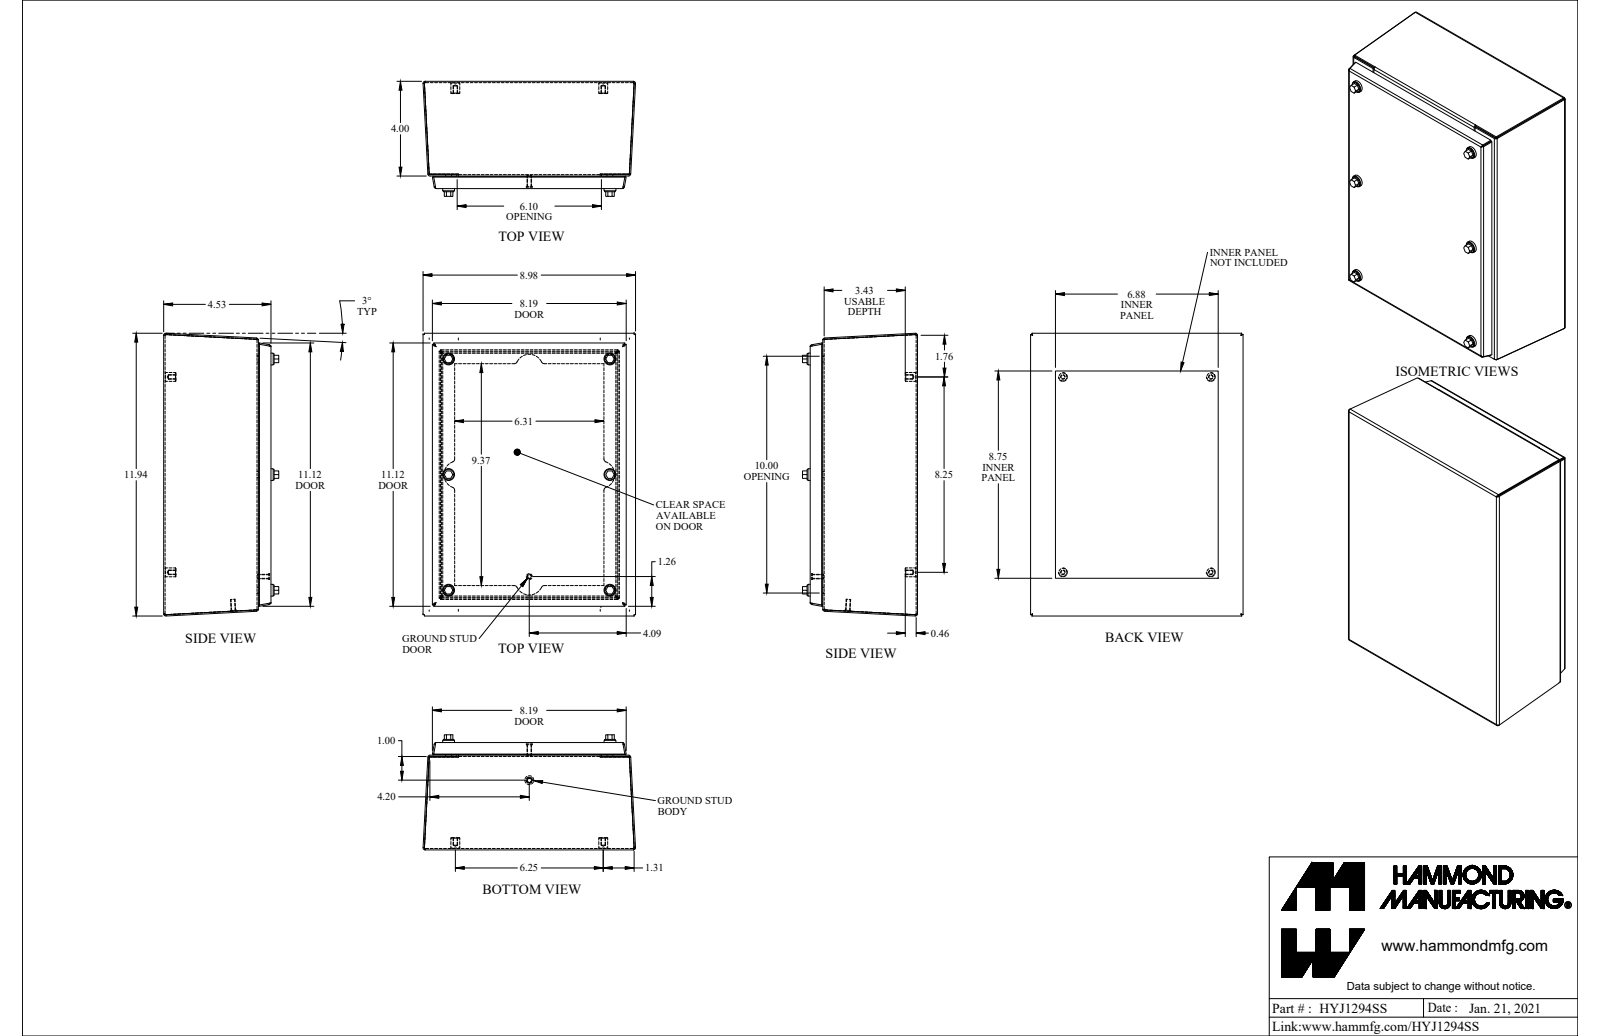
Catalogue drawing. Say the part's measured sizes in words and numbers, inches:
The part is named "HYJ1294SS". Its 3-D file was written by "SolidWorks 2021 (AUTOMOTIVE_DESIGN)". It is 34 solids with 559 faces: 355 planar, 170 cylindrical and 34 other. Overall it measures 11.942 by 8.976 by 4.859 inches. Its volume is 30.49 cubic inches and its surface area 986.8 square inches. Round holes: 6 of diameter 0.065, 6 of diameter 0.235, 6 of diameter 0.239, 6 of diameter 0.24, 6 of diameter 0.25, 6 of diameter 0.253, 4 of diameter 0.156, 4 of diameter 0.4. Round bosses or shafts: 10 of diameter 0.375, 8 of diameter 0.19, 6 of diameter 0.5, 6 of diameter 0.45, 6 of diameter 0.406, 6 of diameter 0.315, 2 of diameter 0.25. Partial cylindrical surfaces (rounded edges, fillets, slot ends): 16 of radius 0.029, 16 of radius 0.086, 8 of radius 0.125, 6 of radius 0.076, 4 of radius 0.055, 4 of radius 0.5, 4 of radius 0.575. The main face-to-face distances are 0.057, 4.418, 4.475, 0.057, 4.532, 4.475, 3.943, 0.475, 4, 0.532. The hole center spacings are 11.911, 4.883, 6.819, 8.387, 9.766, 11.128, 4.883, 8.387.
